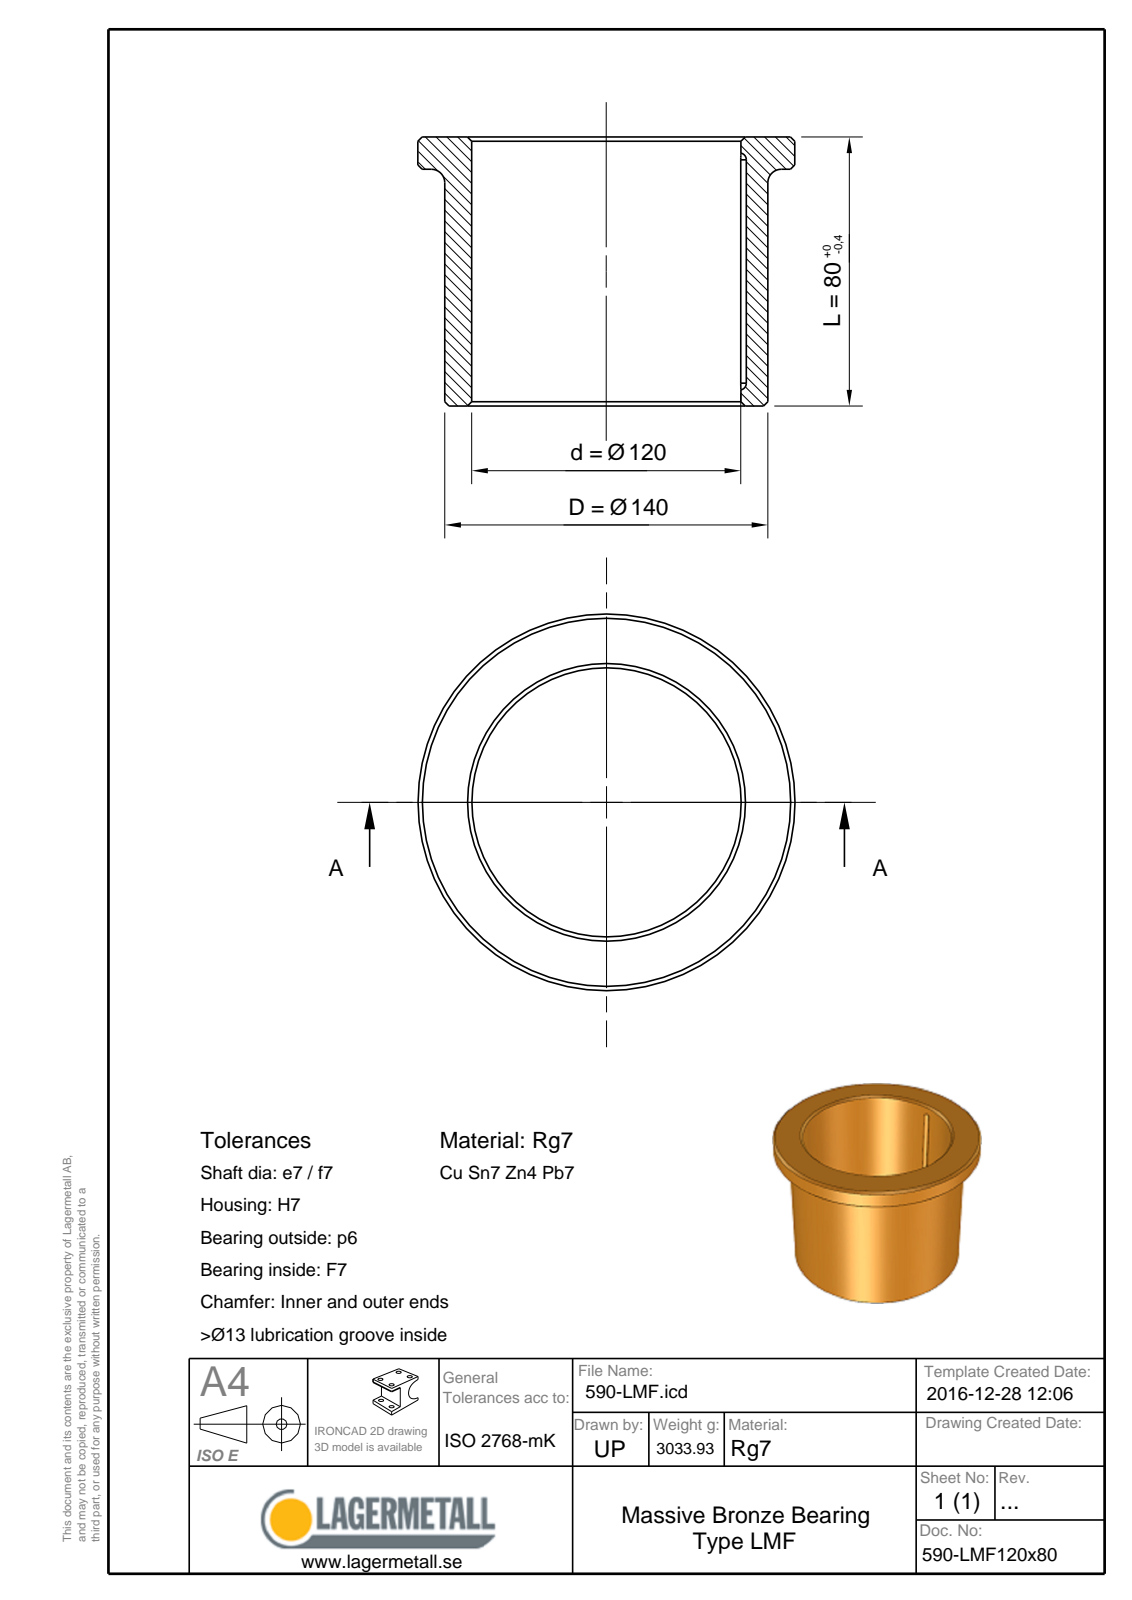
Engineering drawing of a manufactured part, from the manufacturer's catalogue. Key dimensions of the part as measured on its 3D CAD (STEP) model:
Part name (STEP PRODUCT): 590-LMF120x80
STEP written by: Spatial InterOp 3D (CONFIG_CONTROL_DESIGN)
Units: millimetres
Bodies: 1 solid, 17 faces (4 planar, 5 cylindrical, 8 other)
Overall size (bounding box): 150 × 150 × 80
Volume: 344 765 mm³ · Surface area: 76 527 mm²
Round holes (diameter × count): ⌀120 ×1
Round bosses / shafts (diameter × count): ⌀150 ×1, ⌀140 ×1
Partial cylindrical surfaces — rounded edges, fillets, slot ends (radius × count): R1.75 ×2
Main face-to-face distances: 80, 72, 8
